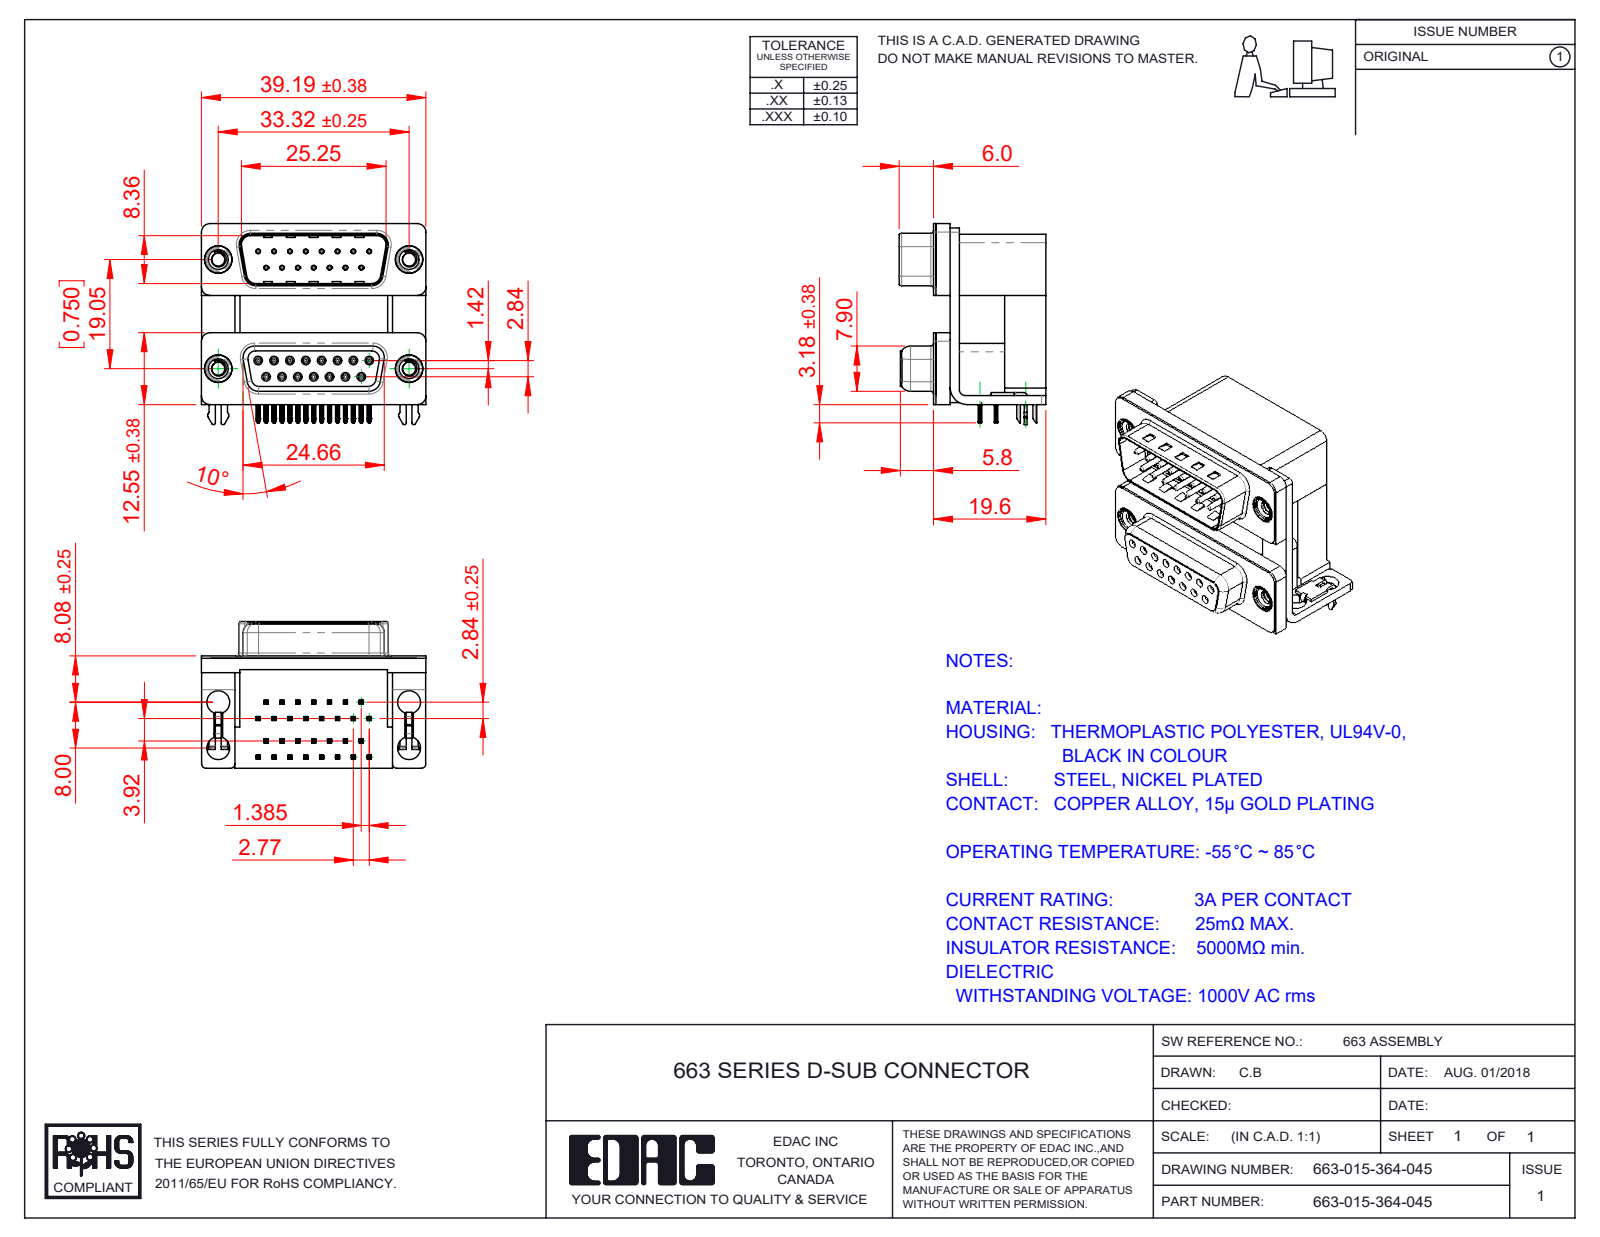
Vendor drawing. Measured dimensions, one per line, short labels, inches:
name: 663 Contact Top Lower; 663 Shell Receptacle_15 Contacts; 663 Threaded Rivet_4-40; 663 Housing Upper_15 Contacts M (+8 more)
written by: SolidWorks 2020 (CONFIG_CONTROL_DESIGN)
unit: in
bodies: 43 solids, 4020 faces (2093 planar, 1044 cylindrical, 883 other)
size: 1.543 × 1.382 × 1.008
volume: 0.929 in³; area: 26.2 in²
holes: 30× ⌀0.031, 15× ⌀0.014, 15× ⌀0.035, 8× ⌀0.157, 4× ⌀0.089, 4× ⌀0.138, 4× ⌀0.189, 4× ⌀0.197
bosses: 15× ⌀0.047, 15× ⌀0.03, 4× ⌀0.193, 4× ⌀0.187, 4× ⌀0.154
rounds: 121× R0.004, 66× R0.01, 60× R0.006, 30× R0.005, 30× R0.014, 16× R0.02, 16× R0.059, 15× R0.013
face distances: 0.016, 0.756, 0.657, 0.098, 0.283, 0.472, 0.374, 0.421, 0.063, 0.114
hole spacings: 0.124, 0.758, 0.109, 0.781, 0.218, 0.327, 0.75, 0.818
